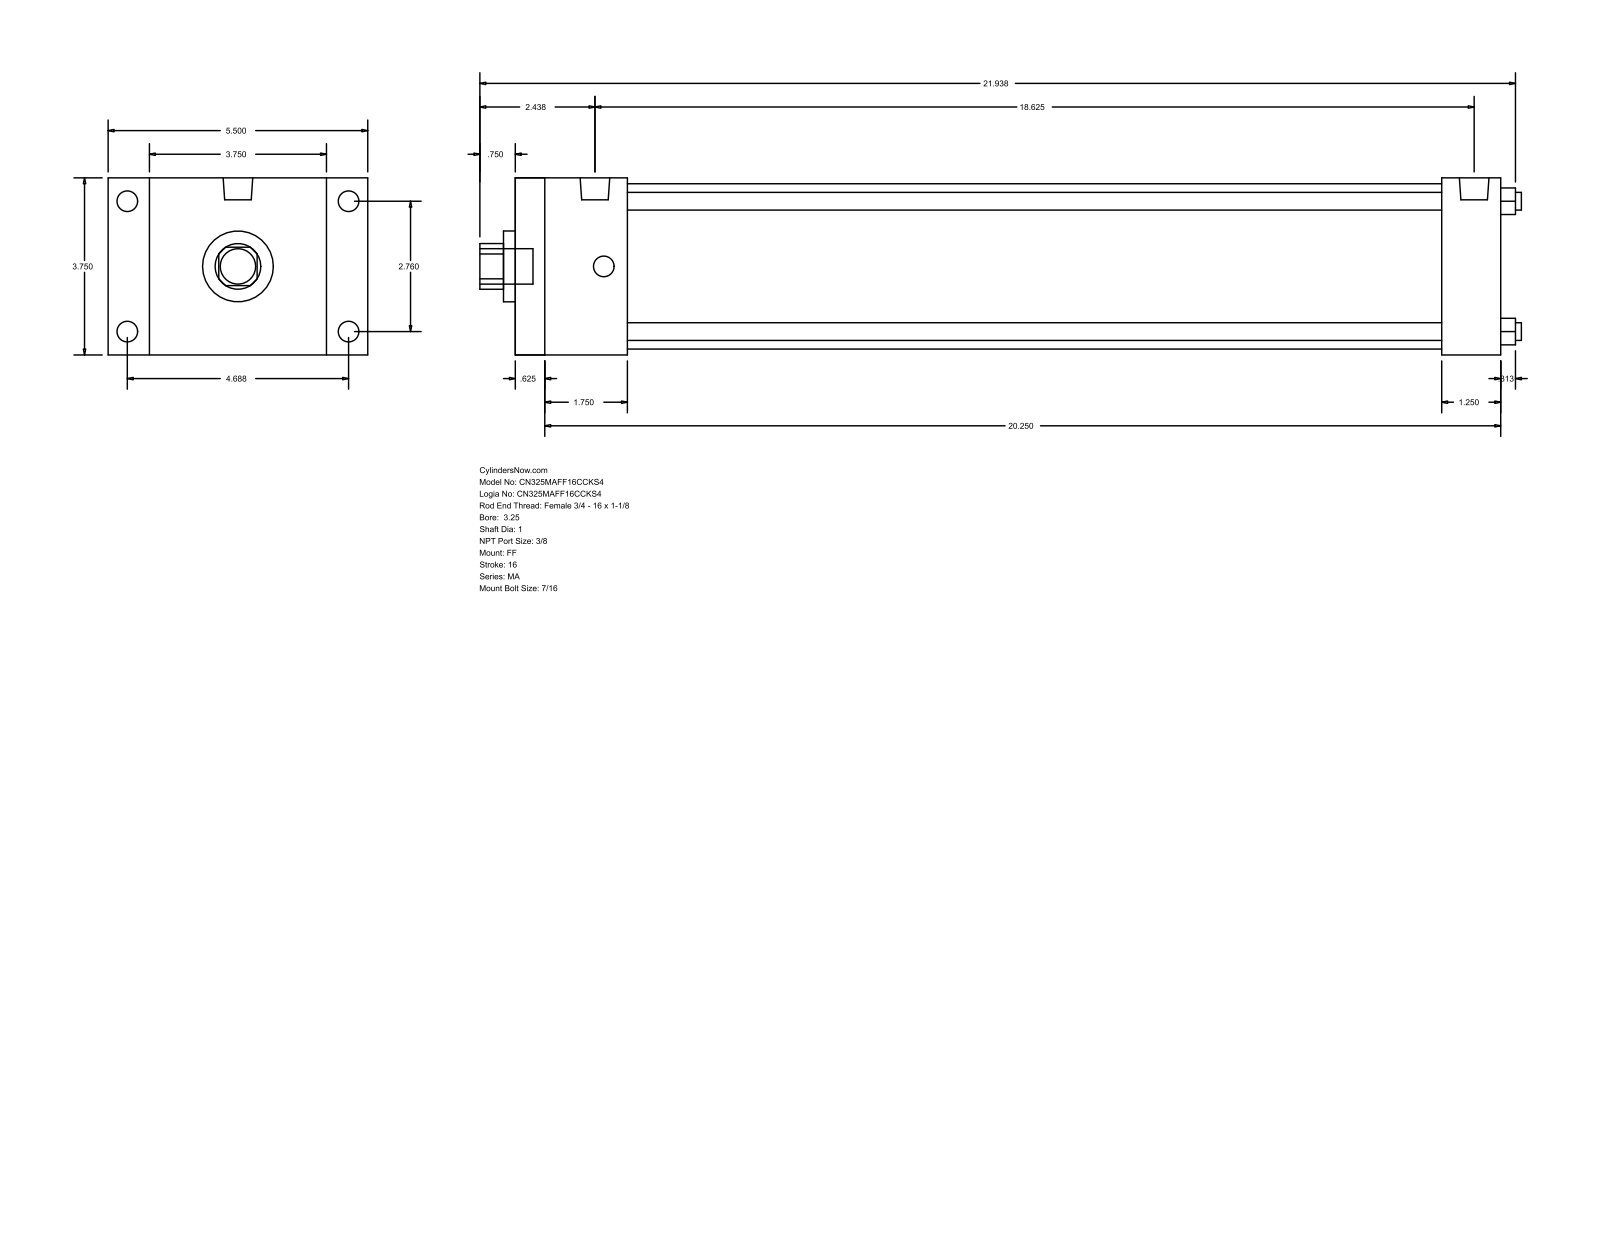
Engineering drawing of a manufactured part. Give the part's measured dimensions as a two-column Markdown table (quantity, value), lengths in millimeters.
| quantity | value |
| --- | --- |
| part name | MA_FF__0325_1 |
| STEP written by | GSSL Pune (CONFIG_CONTROL_DESIGN) |
| units | millimeters |
| bodies | 0 solids, 92 faces (64 planar, 28 cylindrical, 0 other) |
| overall size | 560.39 × 139.7 × 95.25 |
| round holes (diameter × count) | 9.53 × 4, 25.4 × 1, 38.1 × 1, 88.9 × 1 |
| round bosses / shafts (diameter × count) | 11.11 × 8, 15.93 × 2, 19.05 × 1 |
| partial cylindrical surfaces (radius × count) | 12.29 × 1 |
| main face-to-face distances | 95.24, 530.22, 15.87, 514.35, 22.23, 117.47, 60.33, 498.47, 44.46, 482.6 |
| hole center spacings | 49.57, 70.1, 99.14 |
